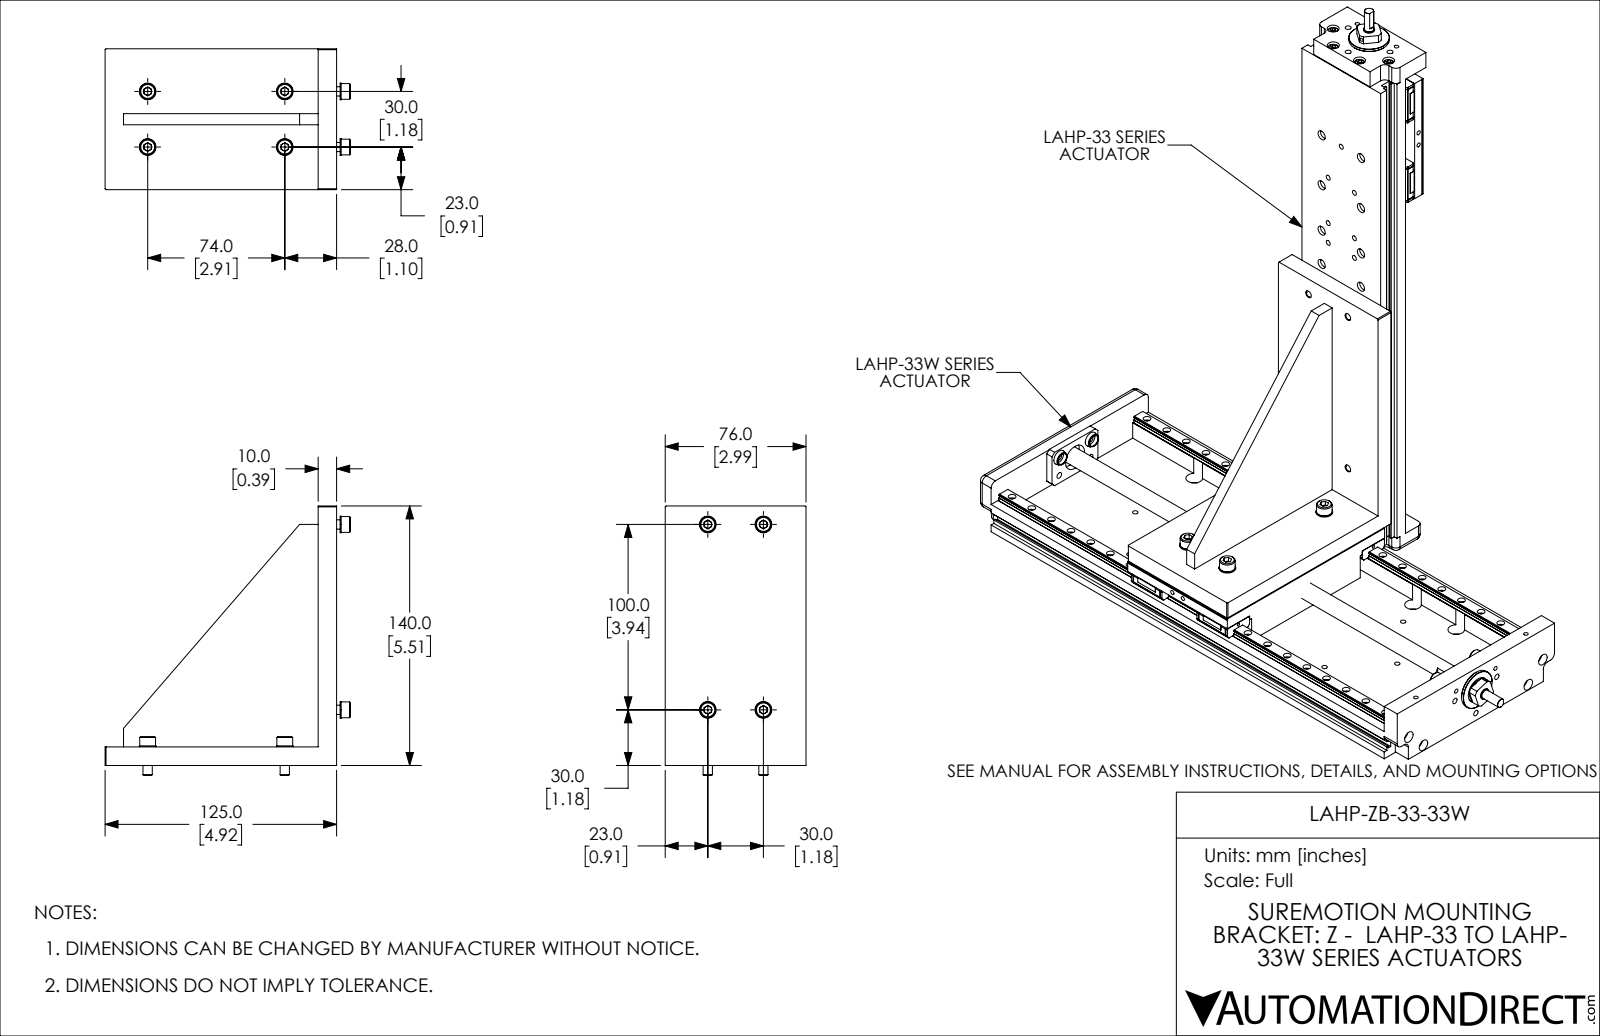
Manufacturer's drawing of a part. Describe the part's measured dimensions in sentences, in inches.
The part is named "LAHP-ZB-33-33W". Its 3-D file was written by "SolidWorks 2019 (CONFIG_CONTROL_DESIGN)". It is 17 solids with 297 faces: 153 planar, 80 cylindrical and 64 other. Overall it measures 11.93 by 5.512 by 2.992 inches. Its volume is 14.7 cubic inches and its surface area 101.5 square inches. Round holes: 8 of diameter 0.209, 4 of diameter 0.165, 4 of diameter 0.217. Round bosses or shafts: 8 of diameter 0.354, 8 of diameter 0.335, 8 of diameter 0.197. The main face-to-face distances are 0.394, 0.236, 1.378, 1.614, 2.992, 5.118, 4.528, 5.512, 4.921, 0.024. The hole center spacings are 1.181, 2.913, 3.144, 3.937, 4.11.
